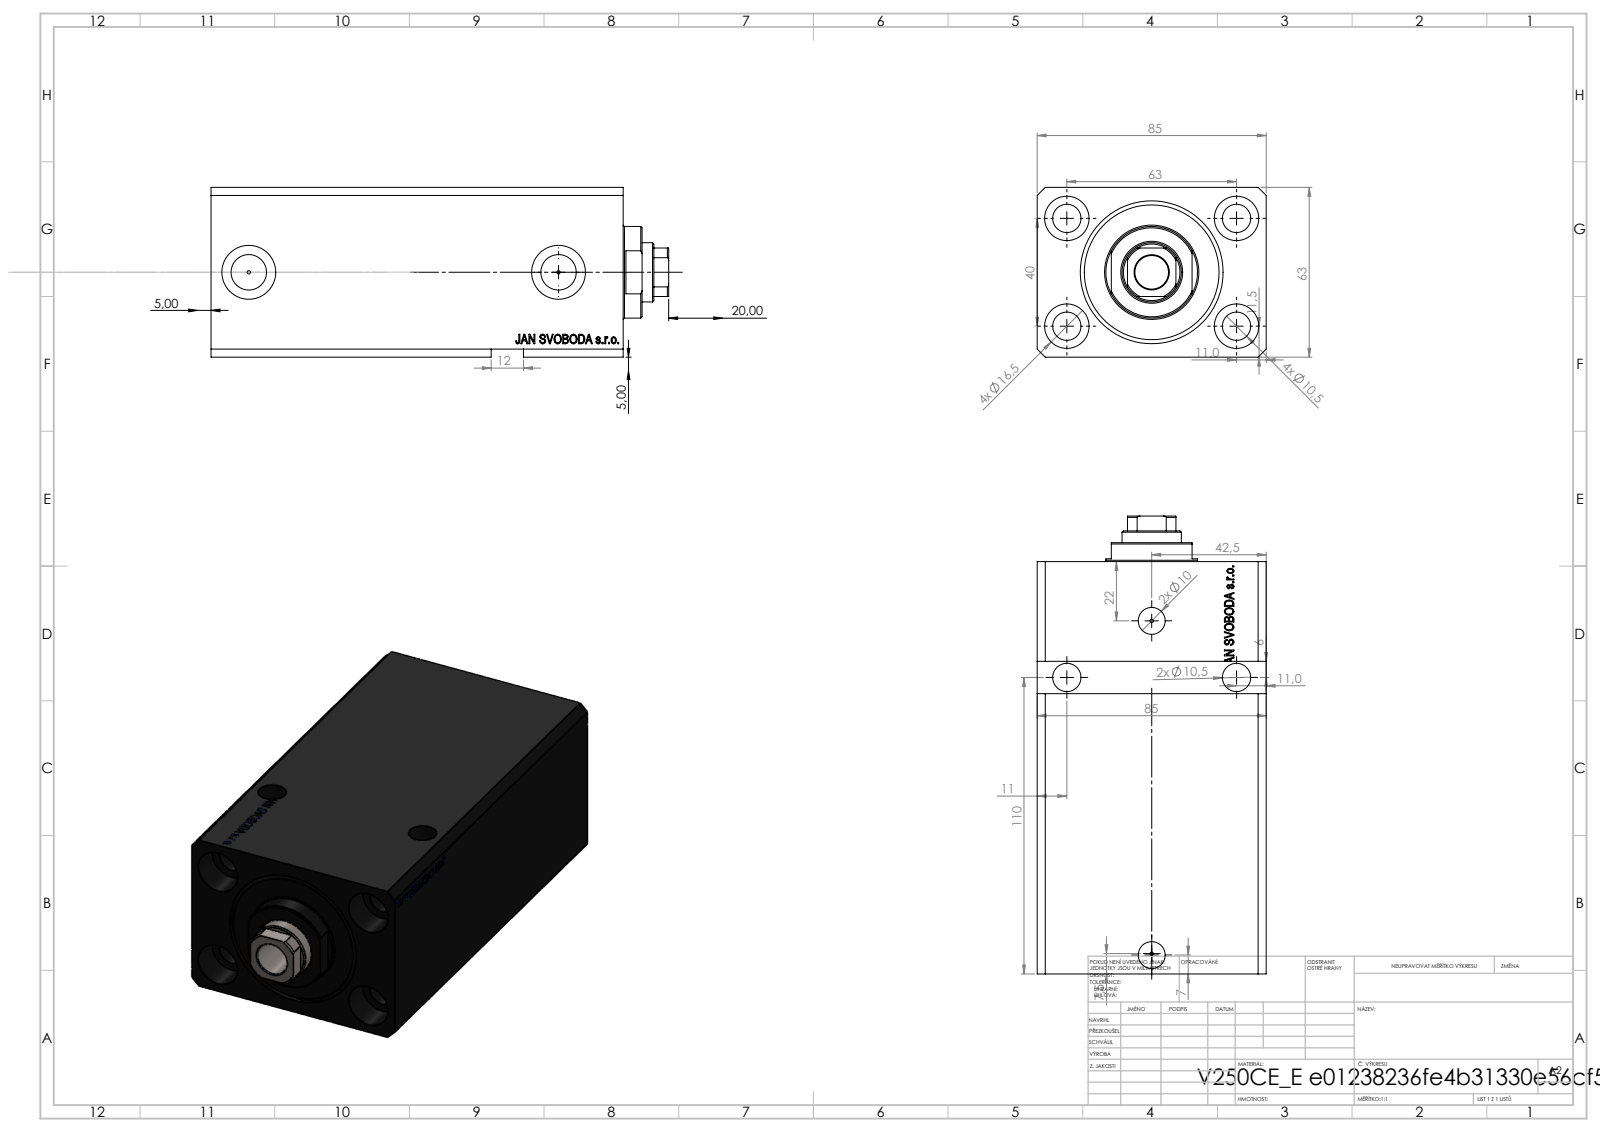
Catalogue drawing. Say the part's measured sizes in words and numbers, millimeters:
The part is named "V250CE_C_VCP; V250CE_VC_E; V250CE_E_Body". Its 3-D file was written by "SolidWorks 2019 (CONFIG_CONTROL_DESIGN)". It is 3 solids with 937 faces: 459 planar, 104 cylindrical and 374 other. Overall it measures 170 by 85 by 63 millimeters. Its volume is 666 198 cubic millimeters and its surface area 126 235 square millimeters. Round holes: 8 of diameter 10.5, 4 of diameter 1.25, 4 of diameter 16.5, 2 of diameter 10, 2 of diameter 13.16, 2 of diameter 20, 1 of diameter 12.5, 1 of diameter 22, 1 of diameter 40, 1 of diameter 53. Round bosses or shafts: 1 of diameter 34. Partial cylindrical surfaces (rounded edges, fillets, slot ends): 1 of radius 10.5. The main face-to-face distances are 63, 85, 153, 17, 136, 11.4, 124.6, 141.6, 56, 60. The hole center spacings are 37.31, 63, 37.86, 40, 41.8, 42.15, 74.63, 75.
